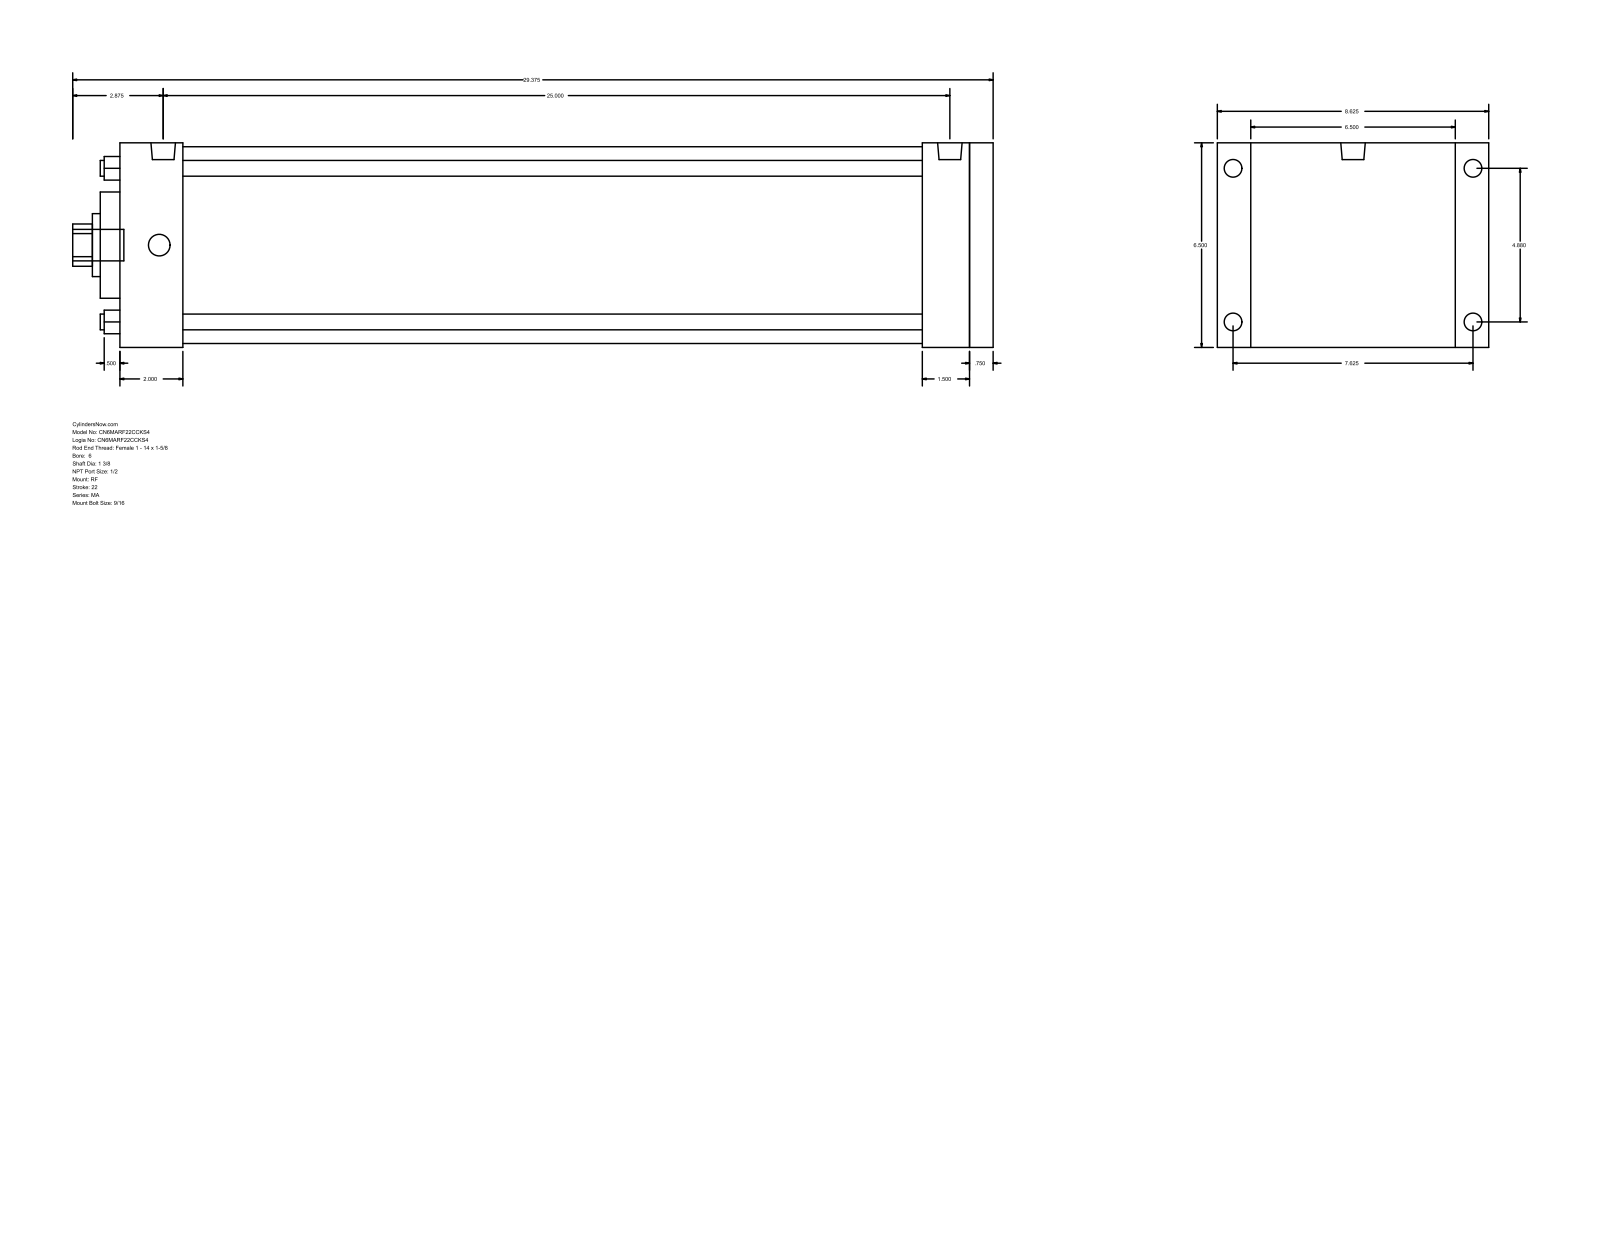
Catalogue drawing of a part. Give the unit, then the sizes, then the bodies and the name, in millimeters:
Units: millimetres
Overall size (bounding box): 746.12 × 219.07 × 165.1
Round holes (diameter × count): ⌀12.7 ×4, ⌀34.92 ×1, ⌀50.8 ×1, ⌀85.72 ×1, ⌀158.75 ×1
Round bosses / shafts (diameter × count): ⌀17.46 ×4, ⌀14.29 ×4, ⌀19.77 ×2, ⌀25.4 ×1
Partial cylindrical surfaces — rounded edges, fillets, slot ends (radius × count): R17.06 ×1
Main face-to-face distances: 165.1, 708.02, 19.04, 688.98, 38.1, 50.8, 638.18, 657.22, 650.88, 600.08
Hole centre spacings: 87.65, 123.96, 175.31
Bodies: 0 solids, 94 faces (65 planar, 29 cylindrical, 0 other)
Part name (STEP PRODUCT): MA_RF__0600_1.375
STEP written by: GSSL Pune (CONFIG_CONTROL_DESIGN)
